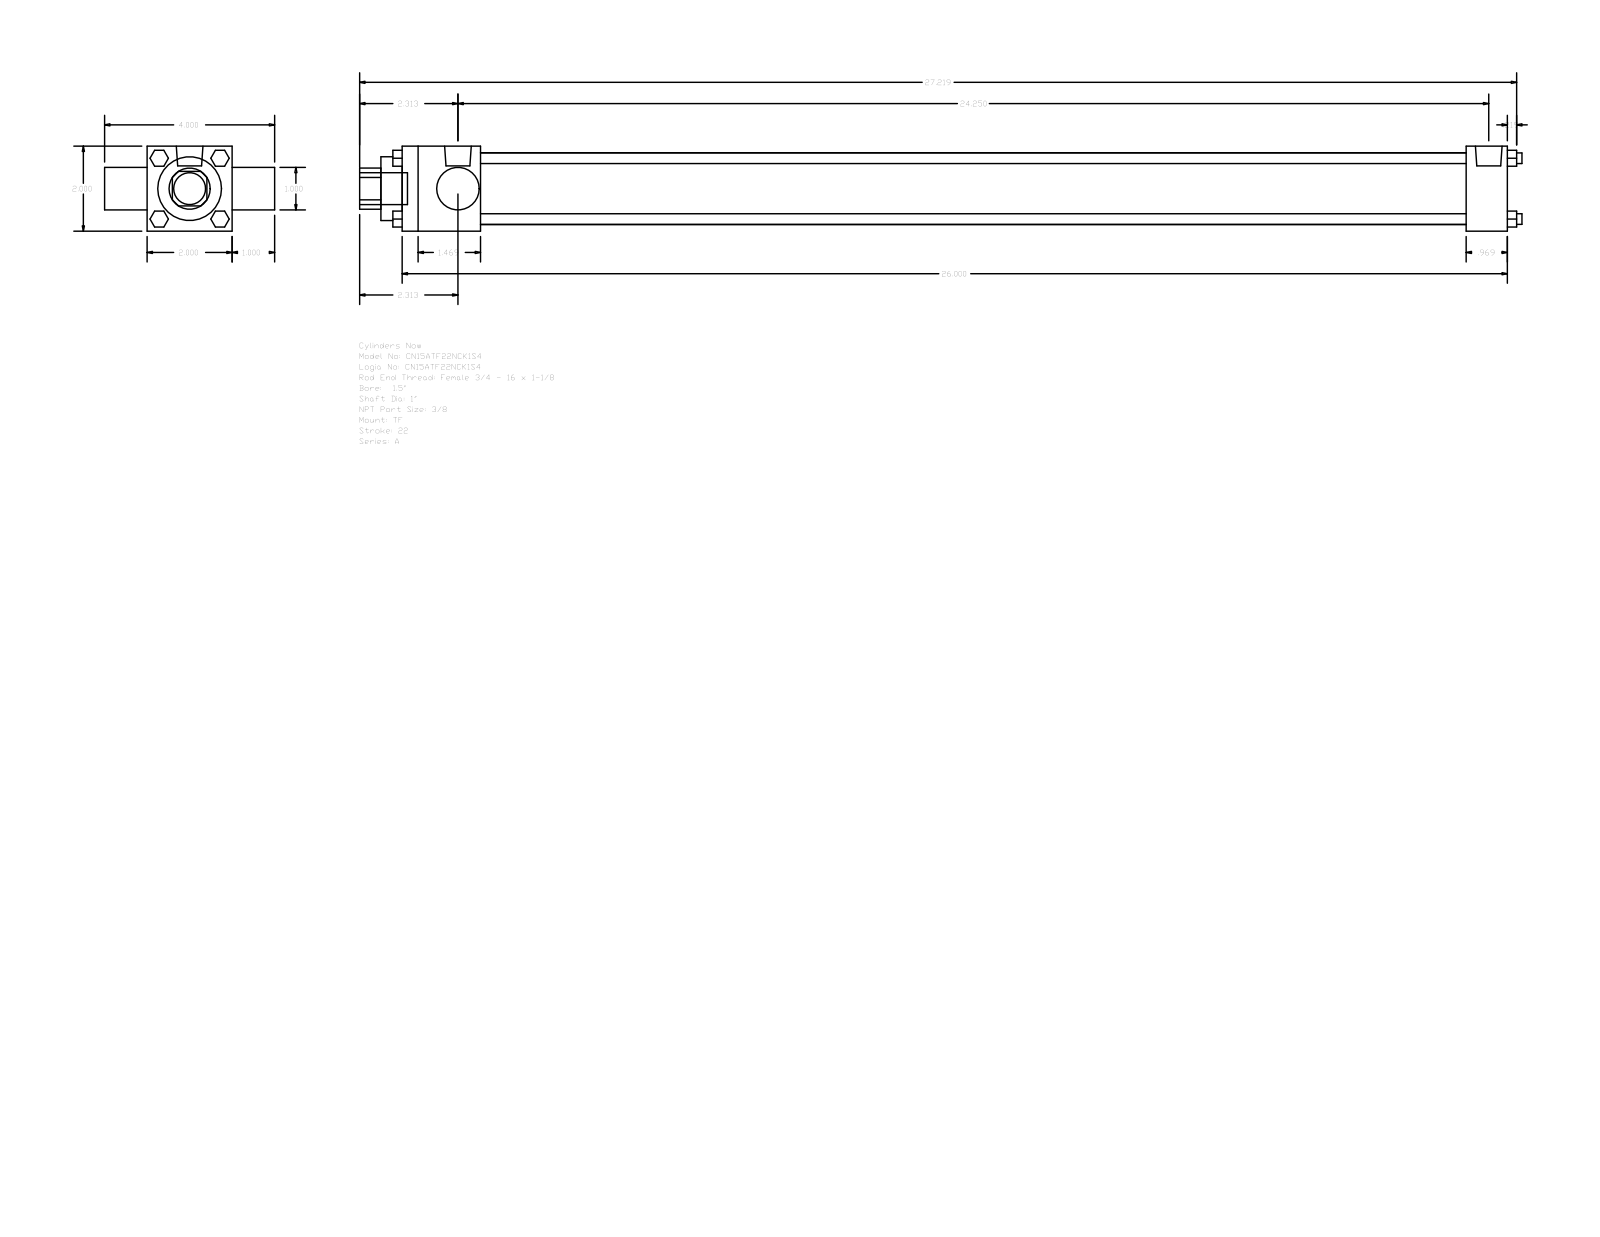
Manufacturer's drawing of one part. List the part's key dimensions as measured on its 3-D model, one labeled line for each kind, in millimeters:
Part name (STEP PRODUCT): A_TF__0150_1
STEP written by: GSSL Pune (CONFIG_CONTROL_DESIGN)
Units: millimetres
Bodies: 0 solids, 120 faces (92 planar, 28 cylindrical, 0 other)
Overall size (bounding box): 694.53 × 101.6 × 50.8
Round holes (diameter × count): ⌀25.4 ×2, ⌀38.1 ×1, ⌀42.93 ×1
Round bosses / shafts (diameter × count): ⌀6.35 ×4, ⌀5.56 ×3, ⌀15.93 ×2, ⌀19.05 ×1
Partial cylindrical surfaces — rounded edges, fillets, slot ends (radius × count): R12.29 ×1
Main face-to-face distances: 50.8, 25.4, 660.4, 76.2, 46.83, 635.79, 588.96, 613.57, 24.61, 12.7
